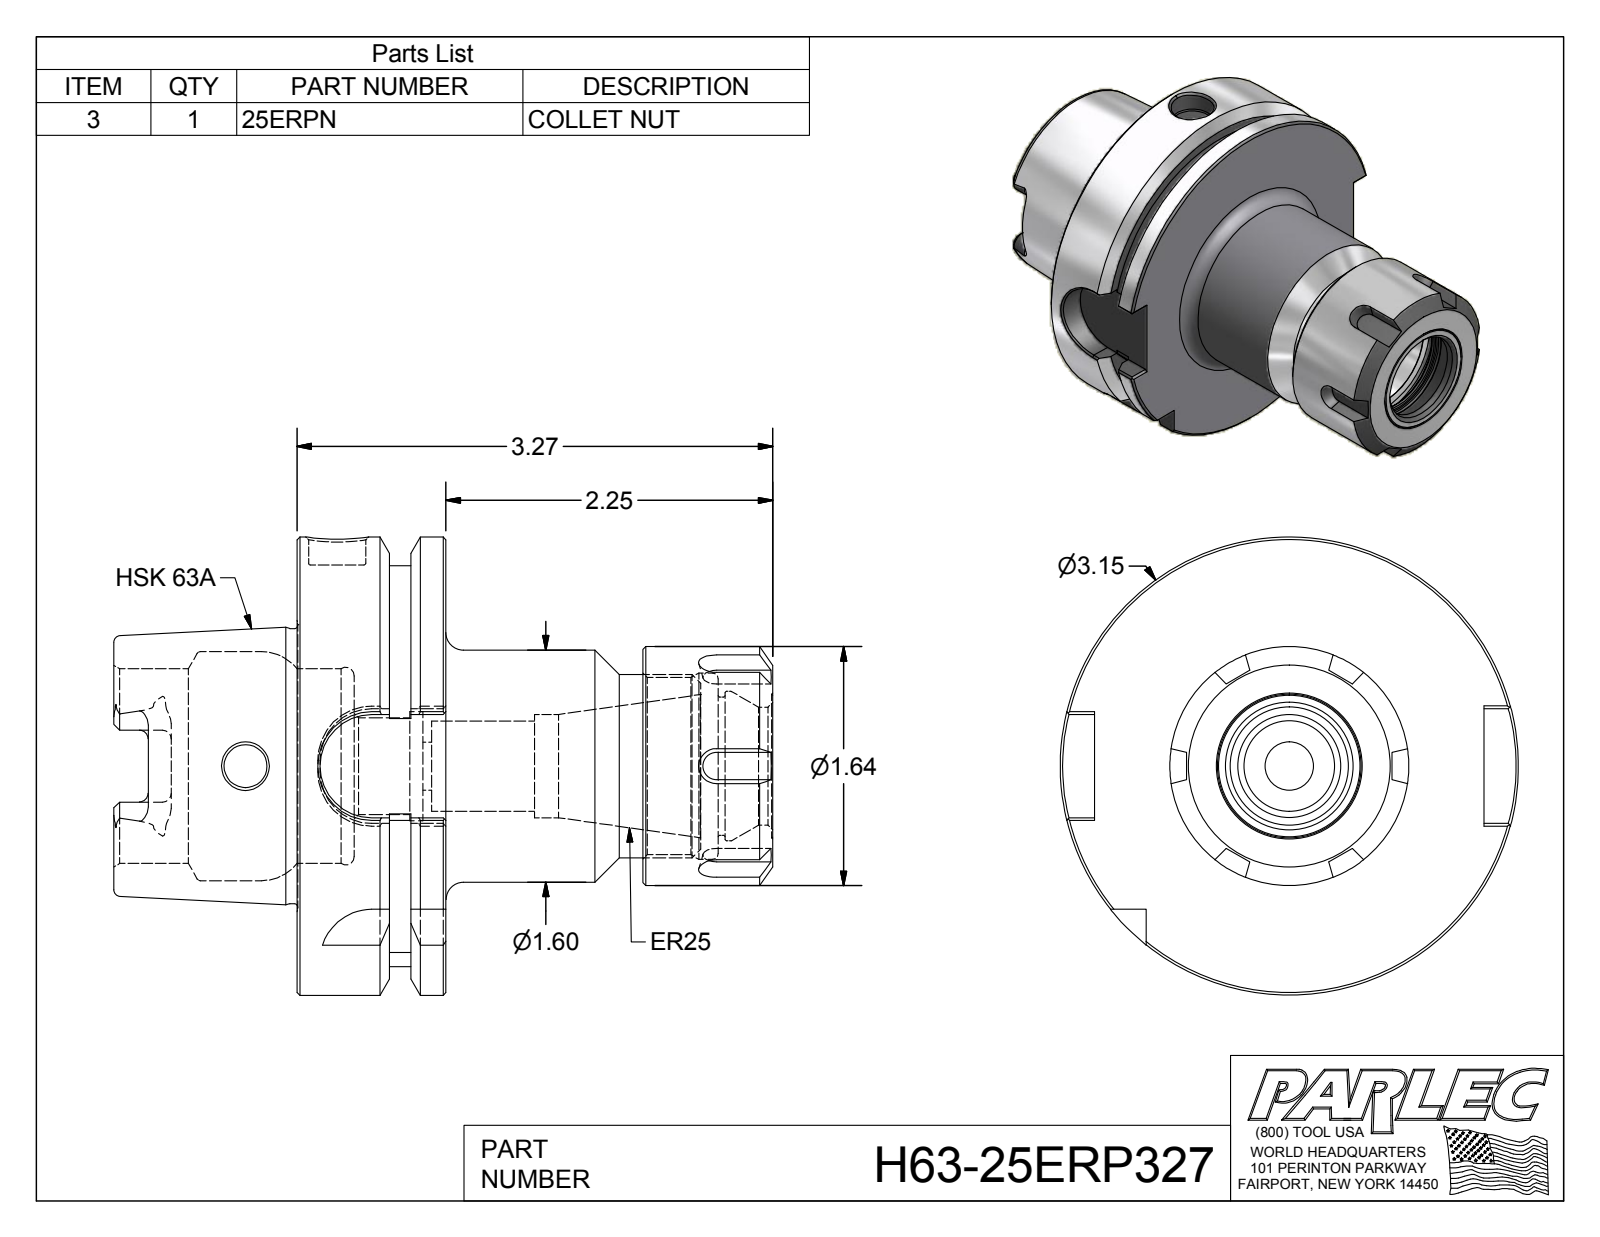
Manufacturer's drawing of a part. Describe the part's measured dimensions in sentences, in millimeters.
The part is named "H63-25ERP327; H63-25ER3-1; 25ERPN". Its 3-D file was written by "Autodesk Inventor 2012 (AUTOMOTIVE_DESIGN)". It is 2 solids with 187 faces: 78 planar, 41 cylindrical and 68 other. Overall it measures 115.1 by 80 by 80 millimeters. Its volume is 178 900 cubic millimeters and its surface area 42 460 square millimeters. Round holes: 1 of diameter 7.5, 1 of diameter 8.4, 1 of diameter 10, 1 of diameter 15.7, 1 of diameter 16.9, 1 of diameter 18, 1 of diameter 19, 1 of diameter 20.6, 1 of diameter 24.1, 1 of diameter 26.1, 1 of diameter 30.9, 1 of diameter 32.5. Round bosses or shafts: 1 of diameter 80, 1 of diameter 48, 1 of diameter 41.7, 1 of diameter 40.5, 1 of diameter 32. Partial cylindrical surfaces (rounded edges, fillets, slot ends): 6 of radius 1.5, 4 of radius 2.9, 4 of radius 9, 1 of radius 35. The main face-to-face distances are 26, 6.1, 9.9, 10, 83.1, 57, 16, 73.1, 19.9, 63.2.
